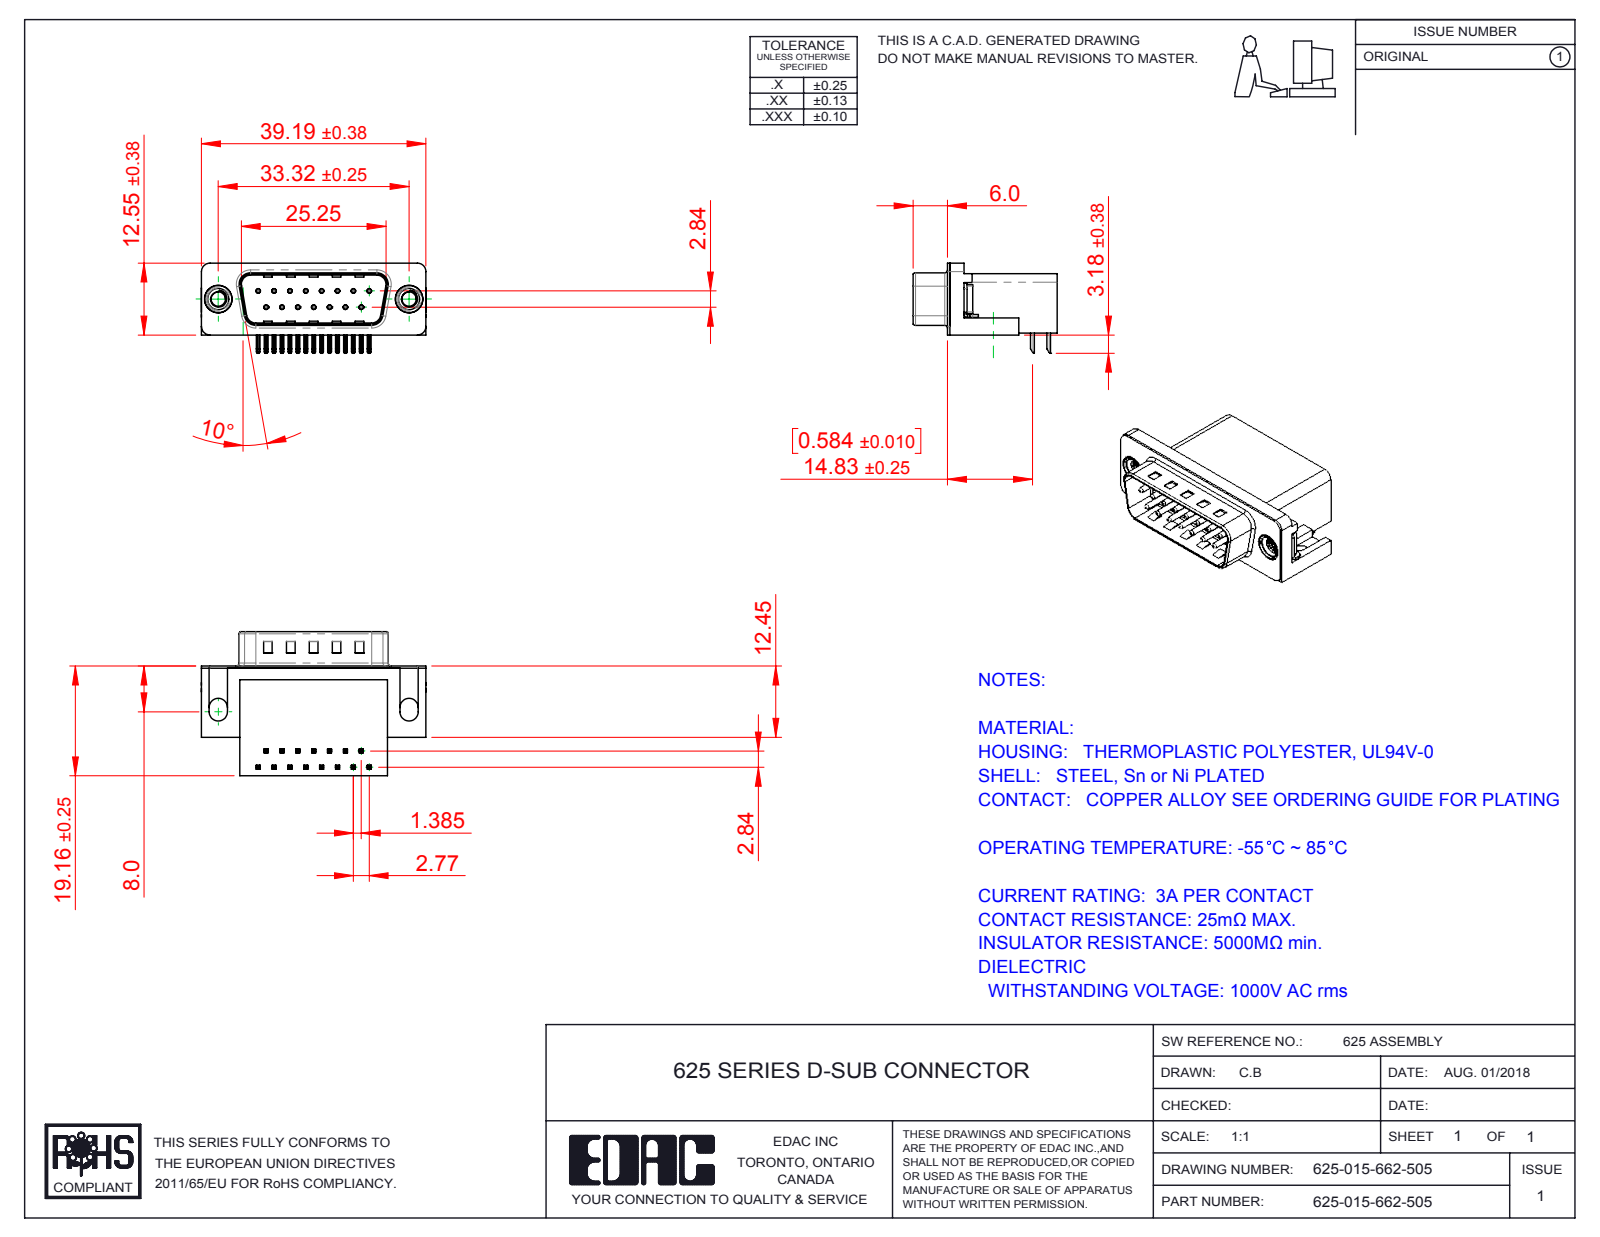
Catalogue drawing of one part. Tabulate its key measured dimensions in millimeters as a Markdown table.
| quantity | value |
| --- | --- |
| part name | 625 Contact Bottom; 625 Non Board Mount; 625 Contact Top; 625 Housing_15 Socket (+3 more) |
| STEP written by | SolidWorks 2016 (CONFIG_CONTROL_DESIGN) |
| units | millimeters |
| bodies | 21 solids, 1477 faces (895 planar, 447 cylindrical, 135 other) |
| overall size | 39.22 × 25.16 × 15.73 |
| volume | 6 210 mm³ |
| surface area | 6 294 mm² |
| round holes (diameter × count) | 0.35 × 15, 0.8 × 15, 2.5 × 2, 4 × 2, 4.8 × 2, 5 × 2 |
| round bosses / shafts (diameter × count) | 0.75 × 15, 4.9 × 2, 4.75 × 2, 3.9 × 2 |
| partial cylindrical surfaces (radius × count) | 0.25 × 68, 0.12 × 30, 1 × 16, 0.5 × 9, 1.6 × 8, 1.5 × 6, 0.9 × 4, 2 × 4 |
| main face-to-face distances | 0.4, 10.35, 18.76, 2.1, 10.46, 19.16, 1.7, 10.86, 8.76, 16.26 |
| hole center spacings | 3.16, 2.77, 5.54, 8.31, 11.08, 5.03, 5.04, 7.48 |
